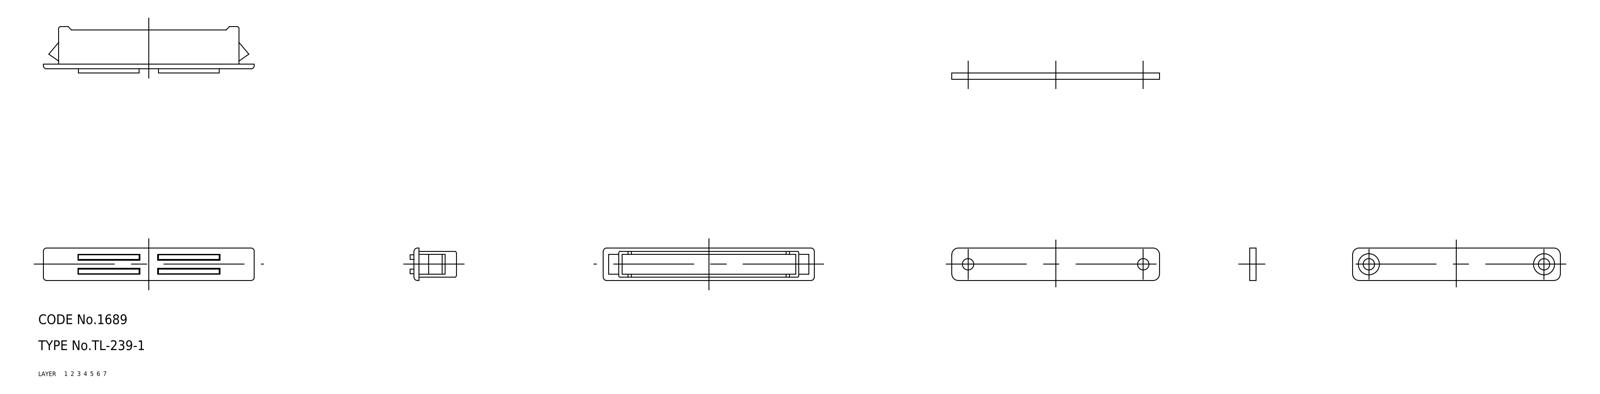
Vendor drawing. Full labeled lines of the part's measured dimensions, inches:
Part name (STEP PRODUCT): attachment; keeper; housing; claw (+1 more)
STEP written by: CADfix (AUTOMOTIVE_DESIGN)
Units: inches
Bodies: 5 solids, 117 faces (0 planar, 0 cylindrical, 117 other)
Overall size (bounding box): 2.559 × 1.267 × 0.394
Volume: 0.332 in³ · Surface area: 13.79 in²
